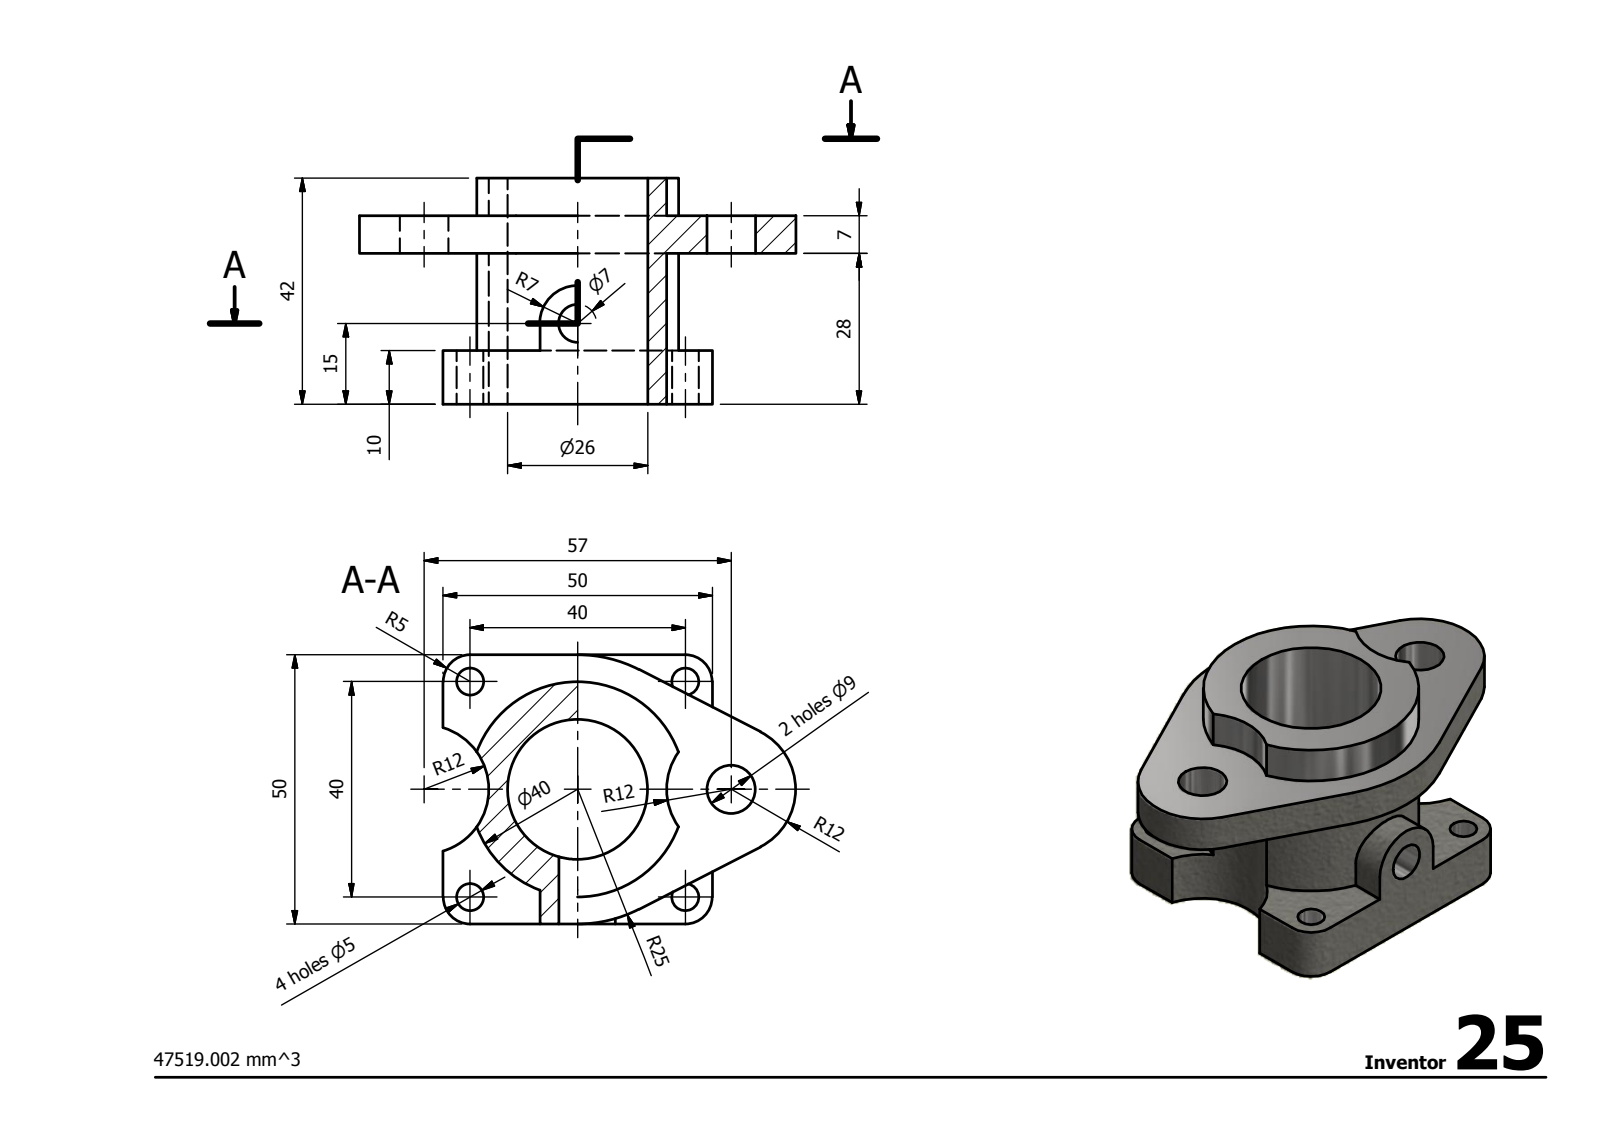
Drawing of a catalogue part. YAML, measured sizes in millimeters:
step_written_by: "Autodesk Inventor 2014 (AUTOMOTIVE_DESIGN)"
units: millimeters
bodies: {solids: 1, faces: 44, planar: 19, cylindrical: 25, other: 0}
overall_size: [81, 50, 42]
volume: 47520
surface_area: 17504
round_holes:
  - {diameter: 5, count: 4}
  - {diameter: 9, count: 2}
  - {diameter: 7, count: 1}
  - {diameter: 26, count: 1}
partial_cylinders:
  - {radius: 5, count: 4}
  - {radius: 12, count: 2}
  - {radius: 7, count: 1}
  - {radius: 20, count: 1}
  - {radius: 25, count: 1}
face_to_face_distances: [7, 28, 35, 50, 18, 10, 25, 32, 14, 42]
hole_center_spacings: [21.73, 28.28, 40, 52.46, 28.5, 56.57, 57]
